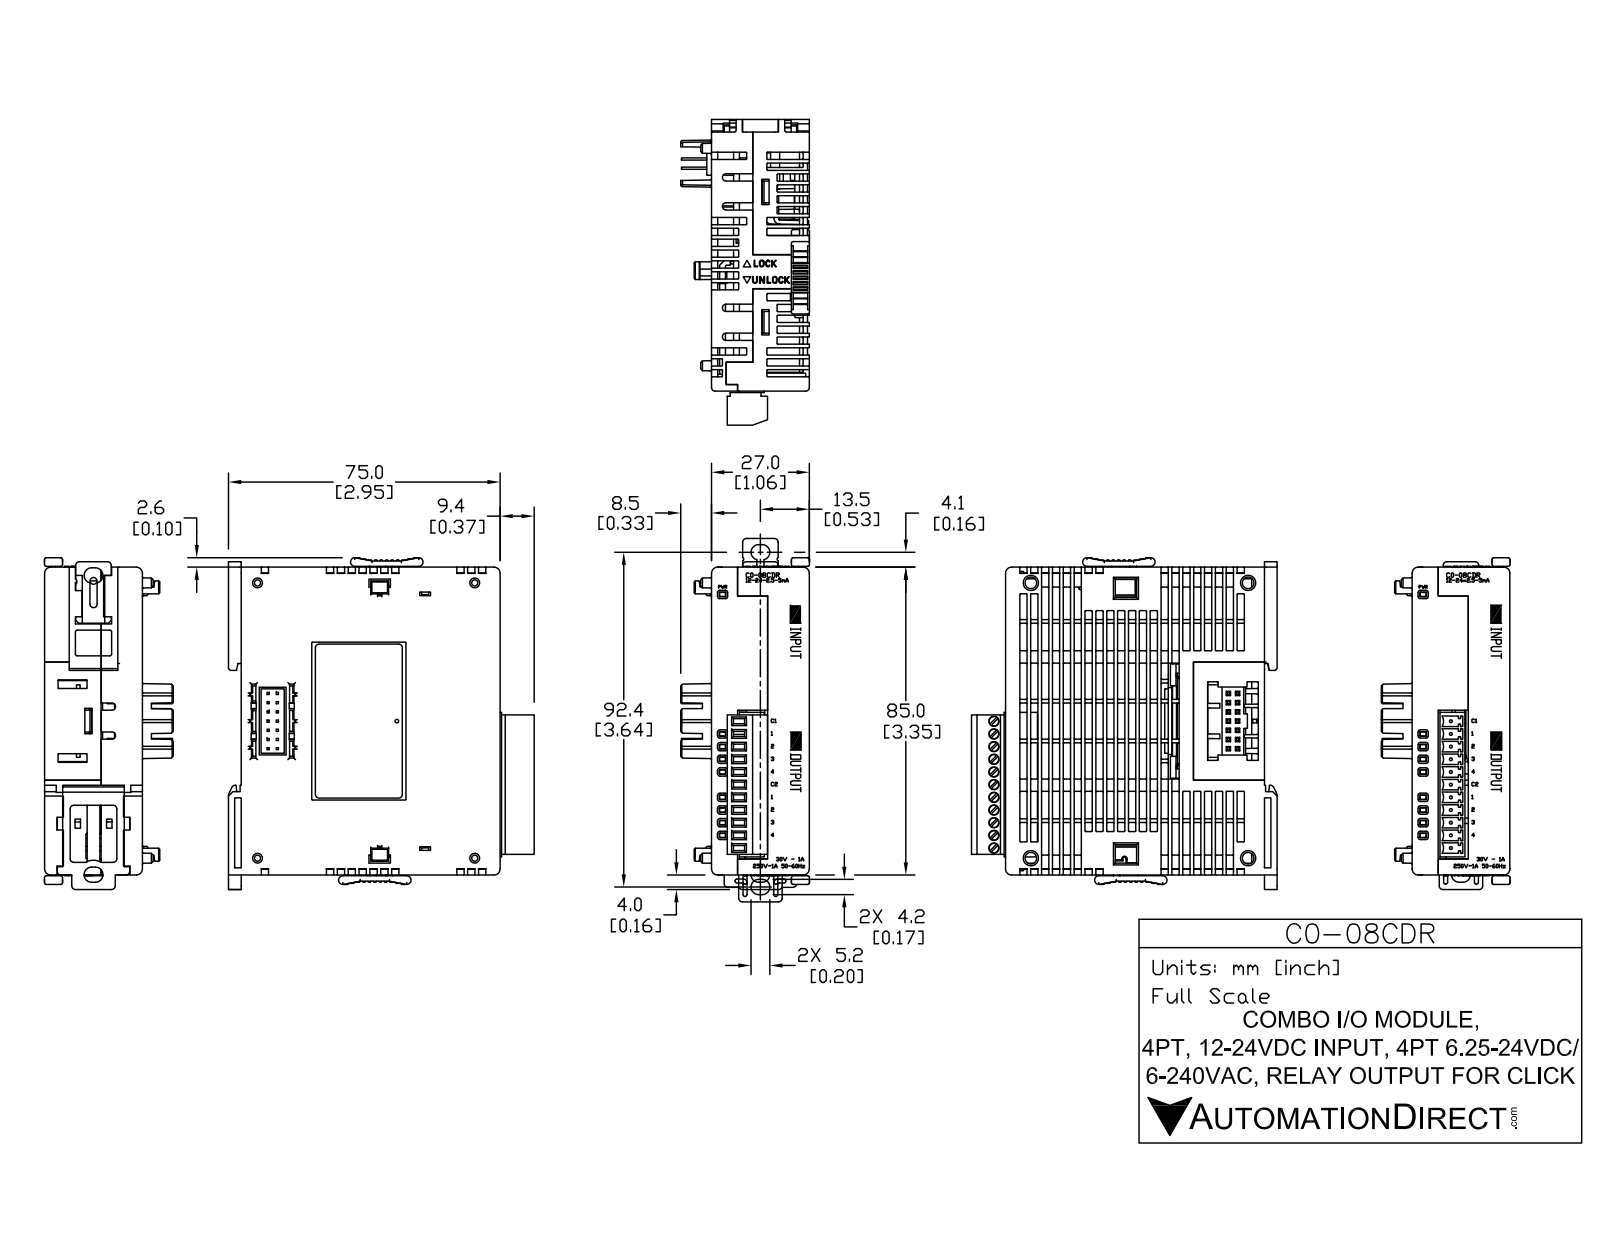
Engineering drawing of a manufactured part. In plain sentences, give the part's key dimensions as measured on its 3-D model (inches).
The part is named "C0-08CDR". Its 3-D file was written by "SolidWorks 2016 (AUTOMOTIVE_DESIGN)". It is 1 solid with 3793 faces: 2676 planar, 968 cylindrical and 149 other. Overall it measures 3.606 by 3.323 by 1.4 inches. Its volume is 9.917 cubic inches and its surface area 49.28 square inches. Round holes: 11 of diameter 0.039, 11 of diameter 0.11, 4 of diameter 0.126, 2 of diameter 0.079. Round bosses or shafts: 11 of diameter 0.102, 1 of diameter 0.075. Partial cylindrical surfaces (rounded edges, fillets, slot ends): 570 of radius 0.008, 43 of radius 0.02, 22 of radius 0.012, 18 of radius 0.039, 12 of radius 0.047, 11 of radius 0.11, 6 of radius 0.067, 4 of radius 0.083. The main face-to-face distances are 1.063, 0.02, 0.02, 1.043, 2.815, 0.067, 3.346, 1.035, 1.056, 3.327. The hole center spacings are 0.138, 0.276, 0.413, 0.551, 0.689, 0.827, 0.965, 1.102.
